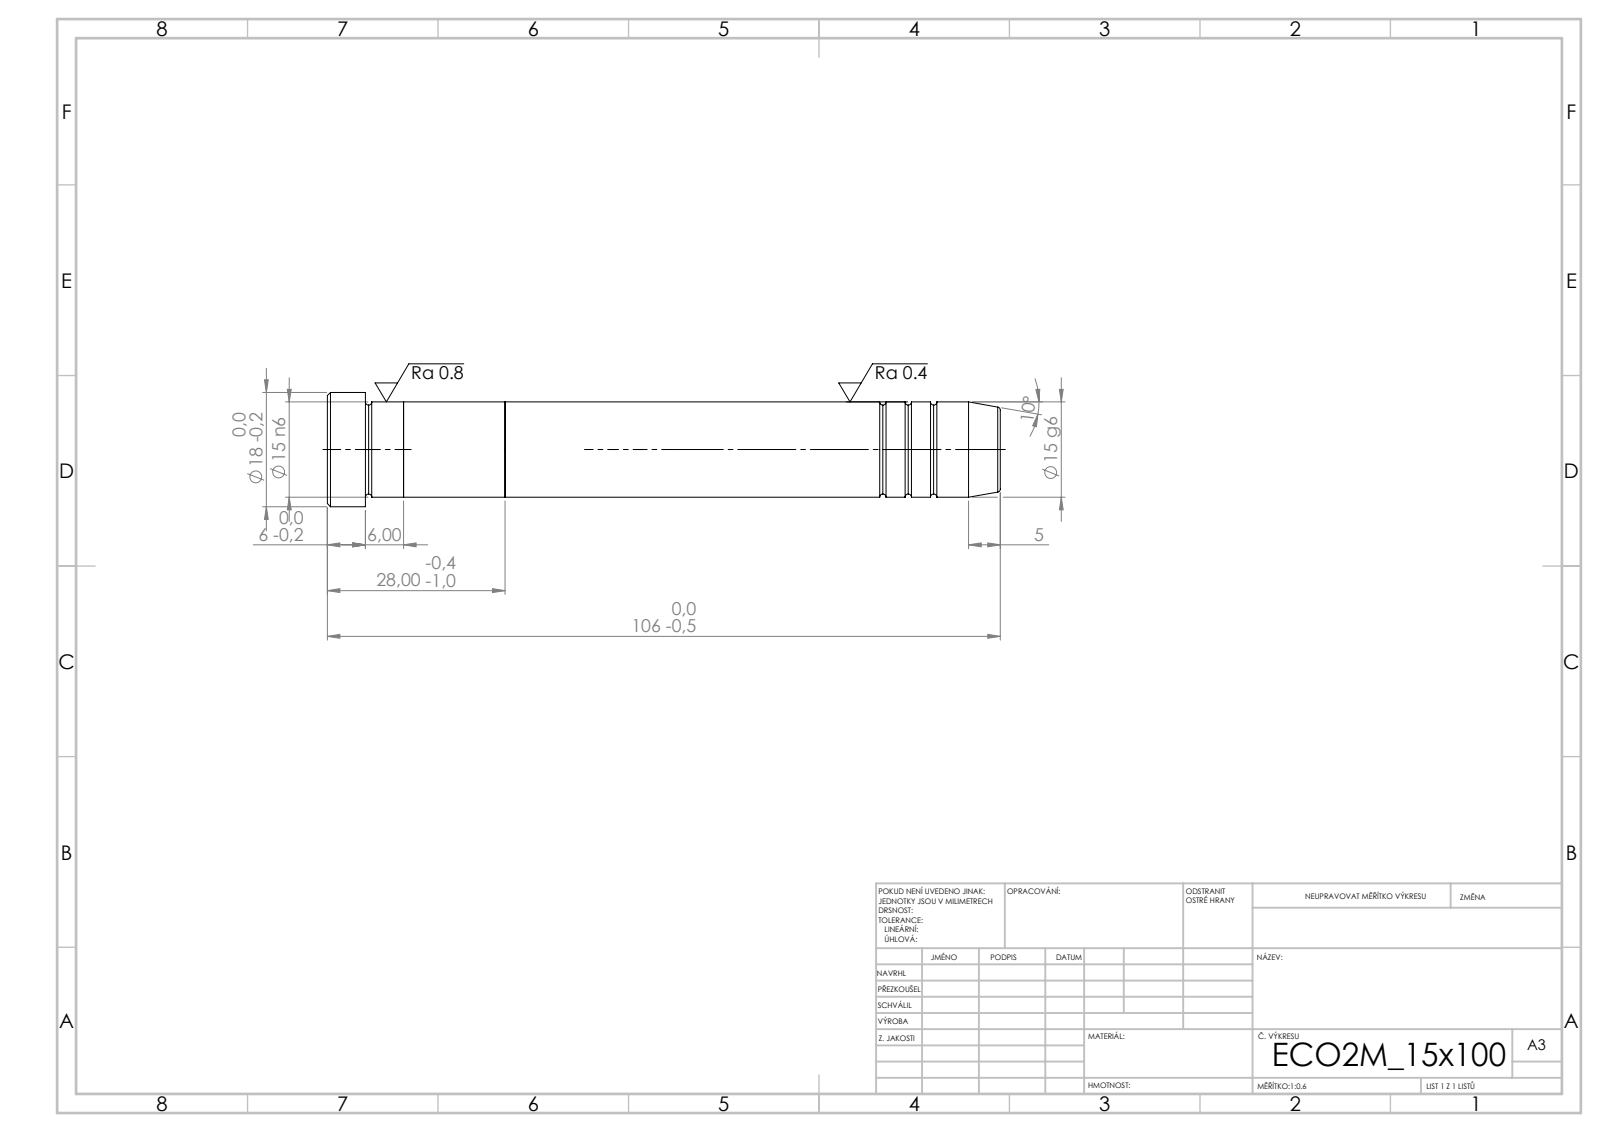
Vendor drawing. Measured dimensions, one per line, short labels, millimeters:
written by: SolidWorks 2019 (CONFIG_CONTROL_DESIGN)
unit: mm
bodies: 3 solids, 43 faces (7 planar, 14 cylindrical, 22 other)
size: 106 × 18 × 18
volume: 19 018 mm³; area: 6 290 mm²
bosses: 1× ⌀18, 1× ⌀15
face distances: 16, 28, 12, 6, 78, 94, 106, 100, 22
